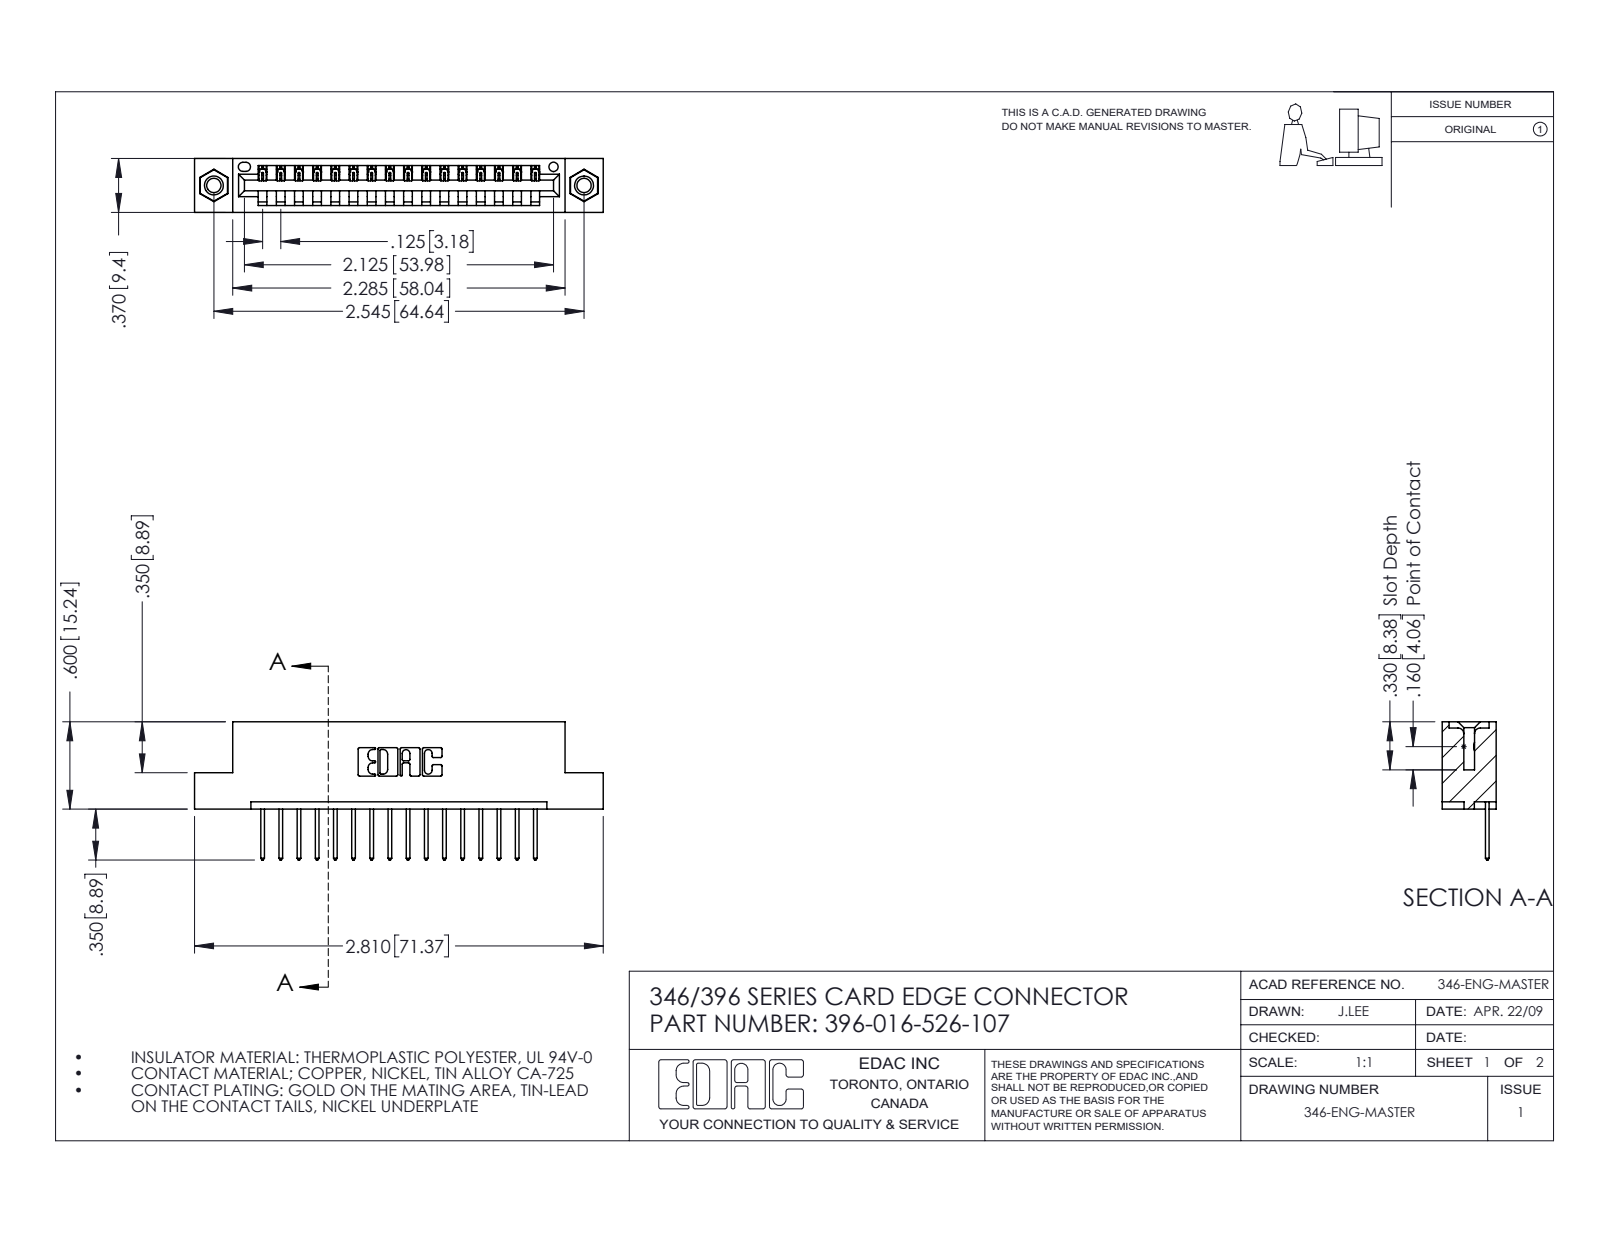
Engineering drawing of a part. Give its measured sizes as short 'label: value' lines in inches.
name: 346 Part_Flush Mounting Lugs - 0.156 Dia-TI; 345-250-001_345-250-005-103; 345-292-001_345-293-126; 396-016-526-107
written by: SolidWorks 2016 (CONFIG_CONTROL_DESIGN)
unit: in
bodies: 19 solids, 1110 faces (748 planar, 346 cylindrical, 16 other)
size: 2.81 × 0.95 × 0.37
volume: 0.404 in³; area: 12.43 in²
holes: 2× ⌀0.098, 2× ⌀0.125, 2× ⌀0.156, 1× ⌀0.064
bosses: 2× ⌀0.155
rounds: 32× R0.006, 32× R0.01, 22× R0.01, 6× R0.007, 6× R0.031, 3× R0.026, 2× R0.031, 2× R0.04
face distances: 0.048, 0.322, 0.25, 0.37, 0.072, 0.298, 0.025, 0.148, 0.222, 0.1
hole spacings: 0.246, 2.338, 2.545
